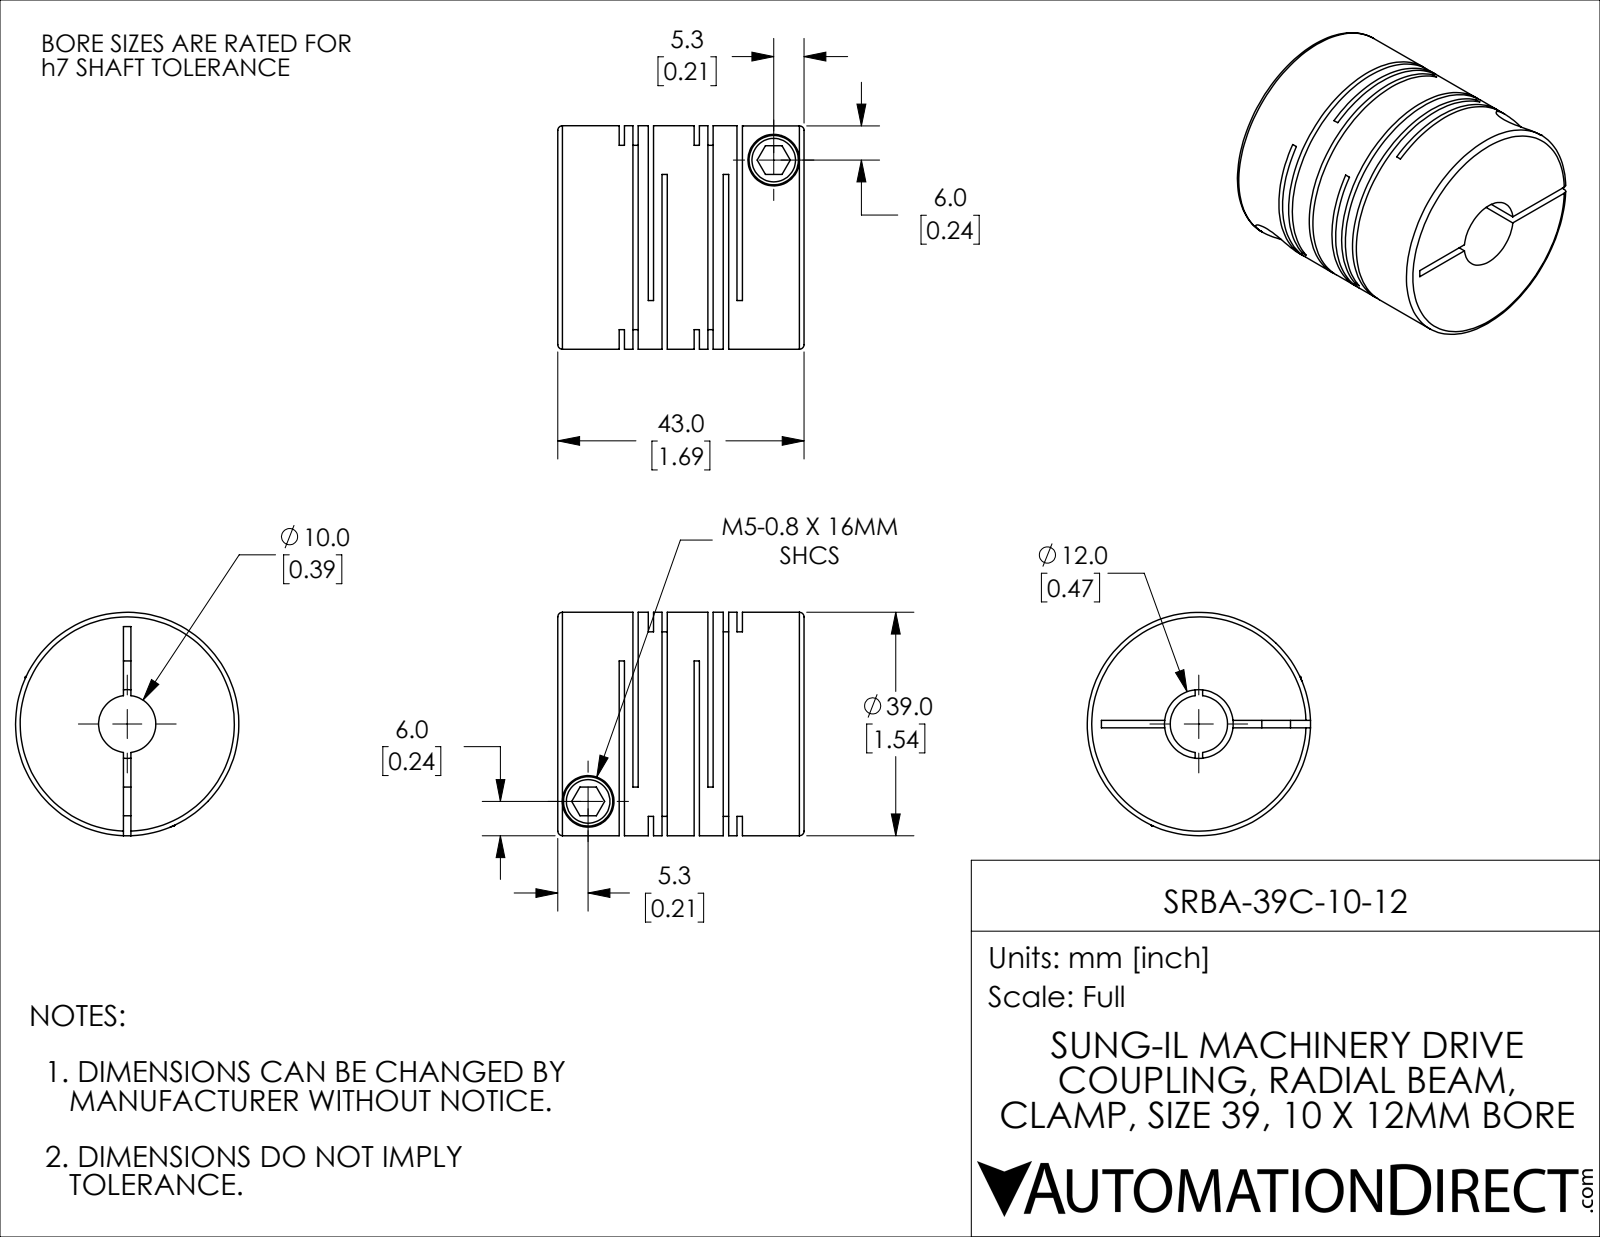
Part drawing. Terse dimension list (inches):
name: SRBA-39C-10-12
written by: SolidWorks 2021 (CONFIG_CONTROL_DESIGN)
unit: in
bodies: 1 solid, 114 faces (60 planar, 42 cylindrical, 12 other)
size: 1.693 × 1.535 × 1.535
volume: 2.362 in³; area: 37.64 in²
holes: 2× ⌀0.197, 2× ⌀0.354, 1× ⌀0.394, 1× ⌀0.472
bosses: 2× ⌀0.339, 1× ⌀1.535
face distances: 0.516, 0.036, 0.094, 0.201, 0.421, 0.552, 0.717, 0.131, 0.61, 0.058
